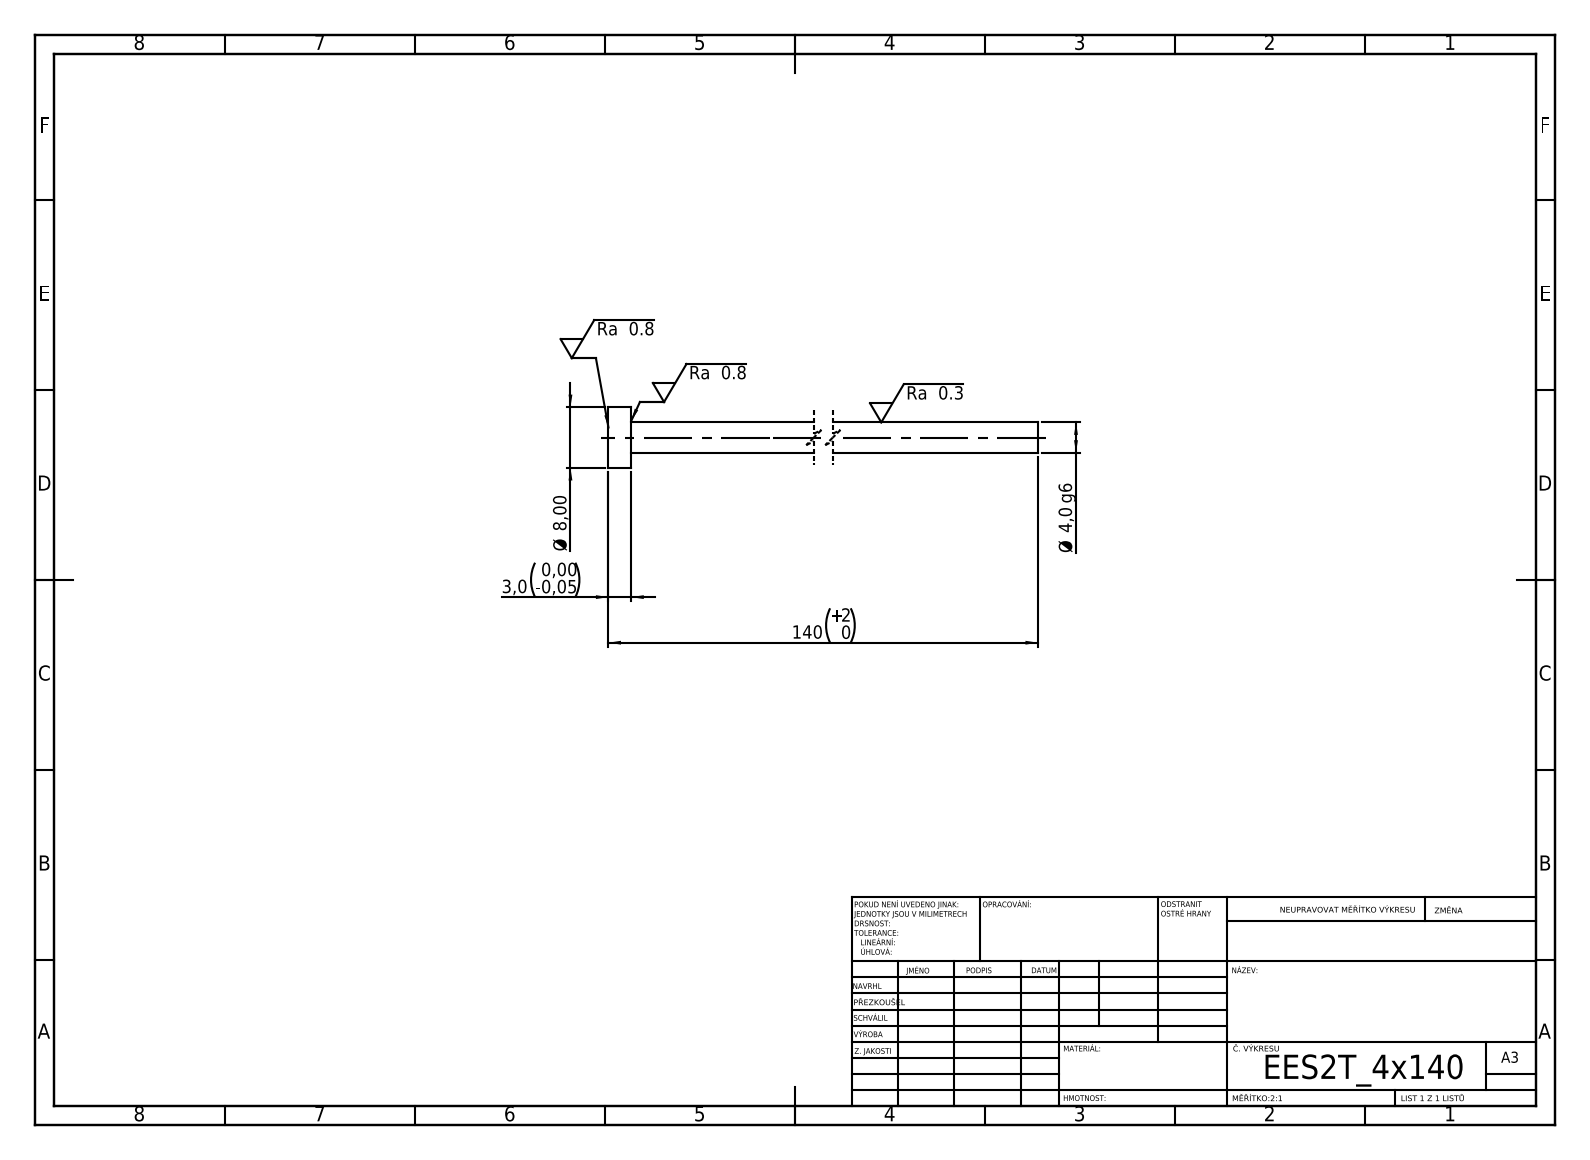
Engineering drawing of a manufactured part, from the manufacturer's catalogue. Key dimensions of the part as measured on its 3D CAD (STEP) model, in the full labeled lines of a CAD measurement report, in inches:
STEP written by: SolidWorks 2019 (CONFIG_CONTROL_DESIGN)
Units: inches
Bodies: 1 solid, 7 faces (3 planar, 4 cylindrical, 0 other)
Overall size (bounding box): 5.512 × 0.315 × 0.315
Volume: 0.114 in³ · Surface area: 2.942 in²
Round bosses / shafts (diameter × count): ⌀0.315 ×1, ⌀0.157 ×1
Main face-to-face distances: 0.118, 5.512, 5.394
